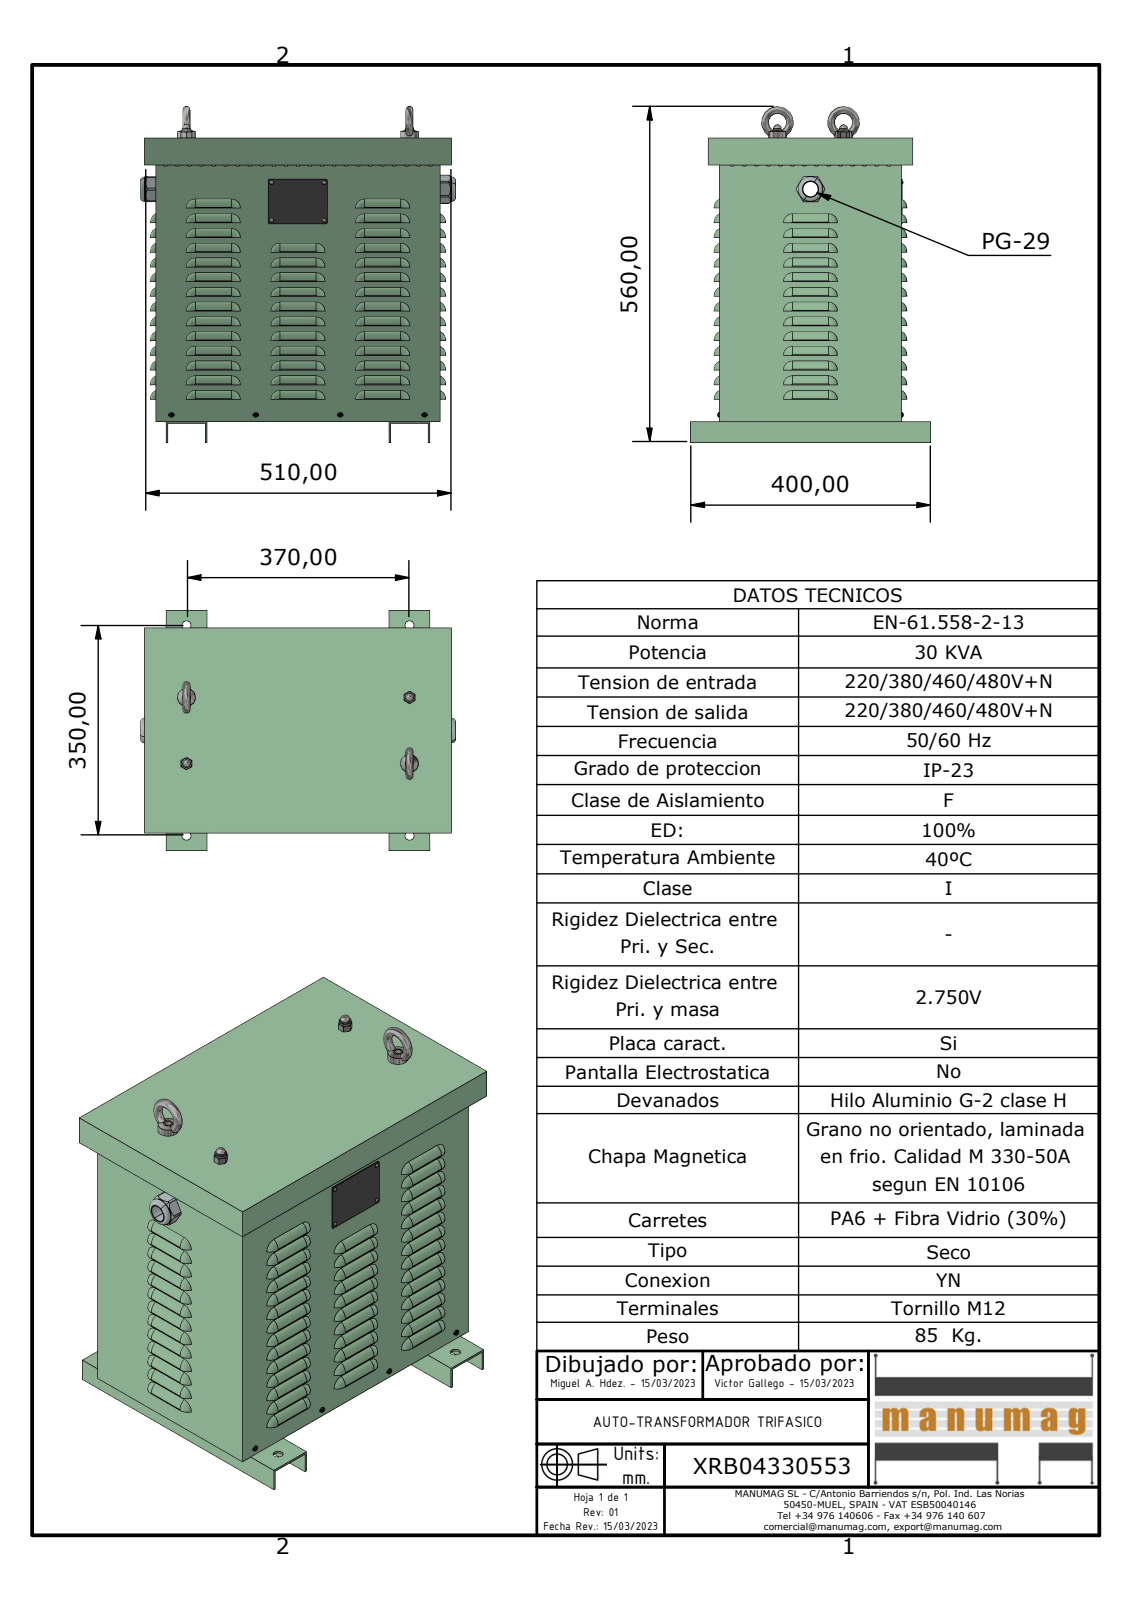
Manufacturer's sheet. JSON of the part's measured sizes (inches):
{"part_name": "XRB04330553; JE030 CUERPO; JE030 BASE; JE030 PATAS (+7 more)", "step_written_by": "Autodesk Inventor 2023 (AUTOMOTIVE_DESIGN)", "units": "inches", "bodies": {"solids": 24, "faces": 2363, "planar": 789, "cylindrical": 948, "other": 626}, "overall_size": [22.047, 20.606, 15.748], "volume_in3": 182, "surface_area_in2": 4092, "round_holes": [[0.433, 260], [0.591, 8], [0.157, 4], [0.197, 4], [0.398, 4], [0.551, 4], [0.984, 1], [1.496, 1]], "round_bosses_or_shafts": [[0.157, 4], [0.143, 4], [0.126, 4], [1.181, 2], [0.709, 2], [0.535, 2], [1.606, 1], [1.469, 1]], "partial_cylinders_radius": [[0.551, 104], [0.197, 74], [0.276, 54], [0.591, 54], [0.127, 12], [0.098, 8], [0.079, 4], [0.939, 1]], "face_to_face_distances": [0.079, 18.504, 11.85, 18.583, 18.425, 11.772, 11.929, 0.748, 0.118, 0.827], "hole_center_spacings": [1.25, 2.819, 0.591, 1.102, 2.756, 1.756, 3.903, 5.543]}
